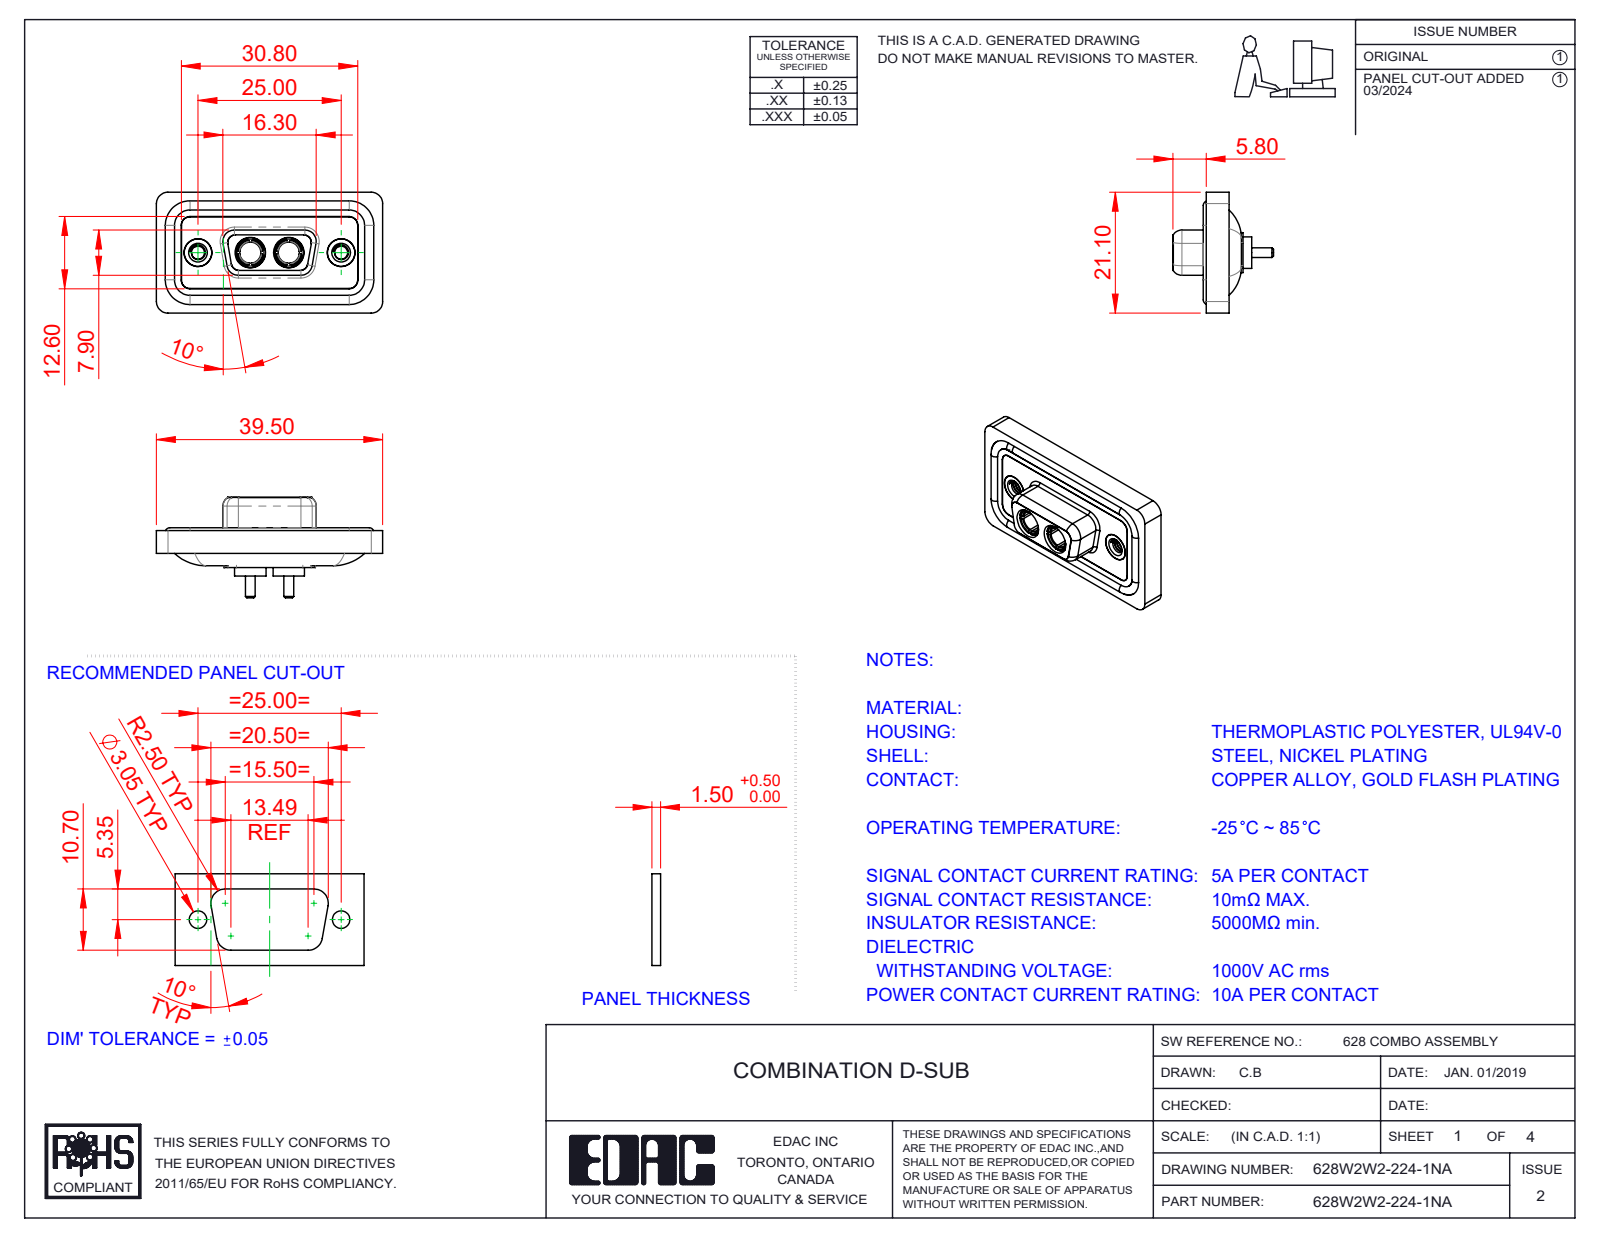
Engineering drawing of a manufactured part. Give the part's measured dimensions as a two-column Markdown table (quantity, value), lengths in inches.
| quantity | value |
| --- | --- |
| part name | 628Combo Shell Front_09 Contacts; 628Combo Threaded Rivet_A; 628Combo Housing_2W2; 628Combo Shell Rear_09 Contacts (+3 more) |
| STEP written by | SolidWorks 2023 (CONFIG_CONTROL_DESIGN) |
| units | inches |
| bodies | 11 solids, 532 faces (163 planar, 236 cylindrical, 133 other) |
| overall size | 1.555 × 0.831 × 0.691 |
| volume | 0.286 in³ |
| surface area | 11.79 in² |
| round holes (diameter × count) | 0.191 × 4, 0.089 × 2, 0.146 × 2, 0.157 × 2, 0.159 × 2, 0.197 × 2, 0.209 × 2 |
| round bosses / shafts (diameter × count) | 0.063 × 4, 0.217 × 2, 0.205 × 2, 0.195 × 2, 0.195 × 2, 0.189 × 2, 0.187 × 2, 0.148 × 2 |
| partial cylindrical surfaces (radius × count) | 0.059 × 22, 0.079 × 18, 0.053 × 8, 0.063 × 8, 0.01 × 4, 0.02 × 4, 0.024 × 4, 0.026 × 4 |
| main face-to-face distances | 0.016, 0.071, 0.043, 0.114, 0.02, 0.063, 0.222, 0.059, 0.293, 0.211 |
| hole center spacings | 0.36, 0.624, 0.265, 0.984 |
